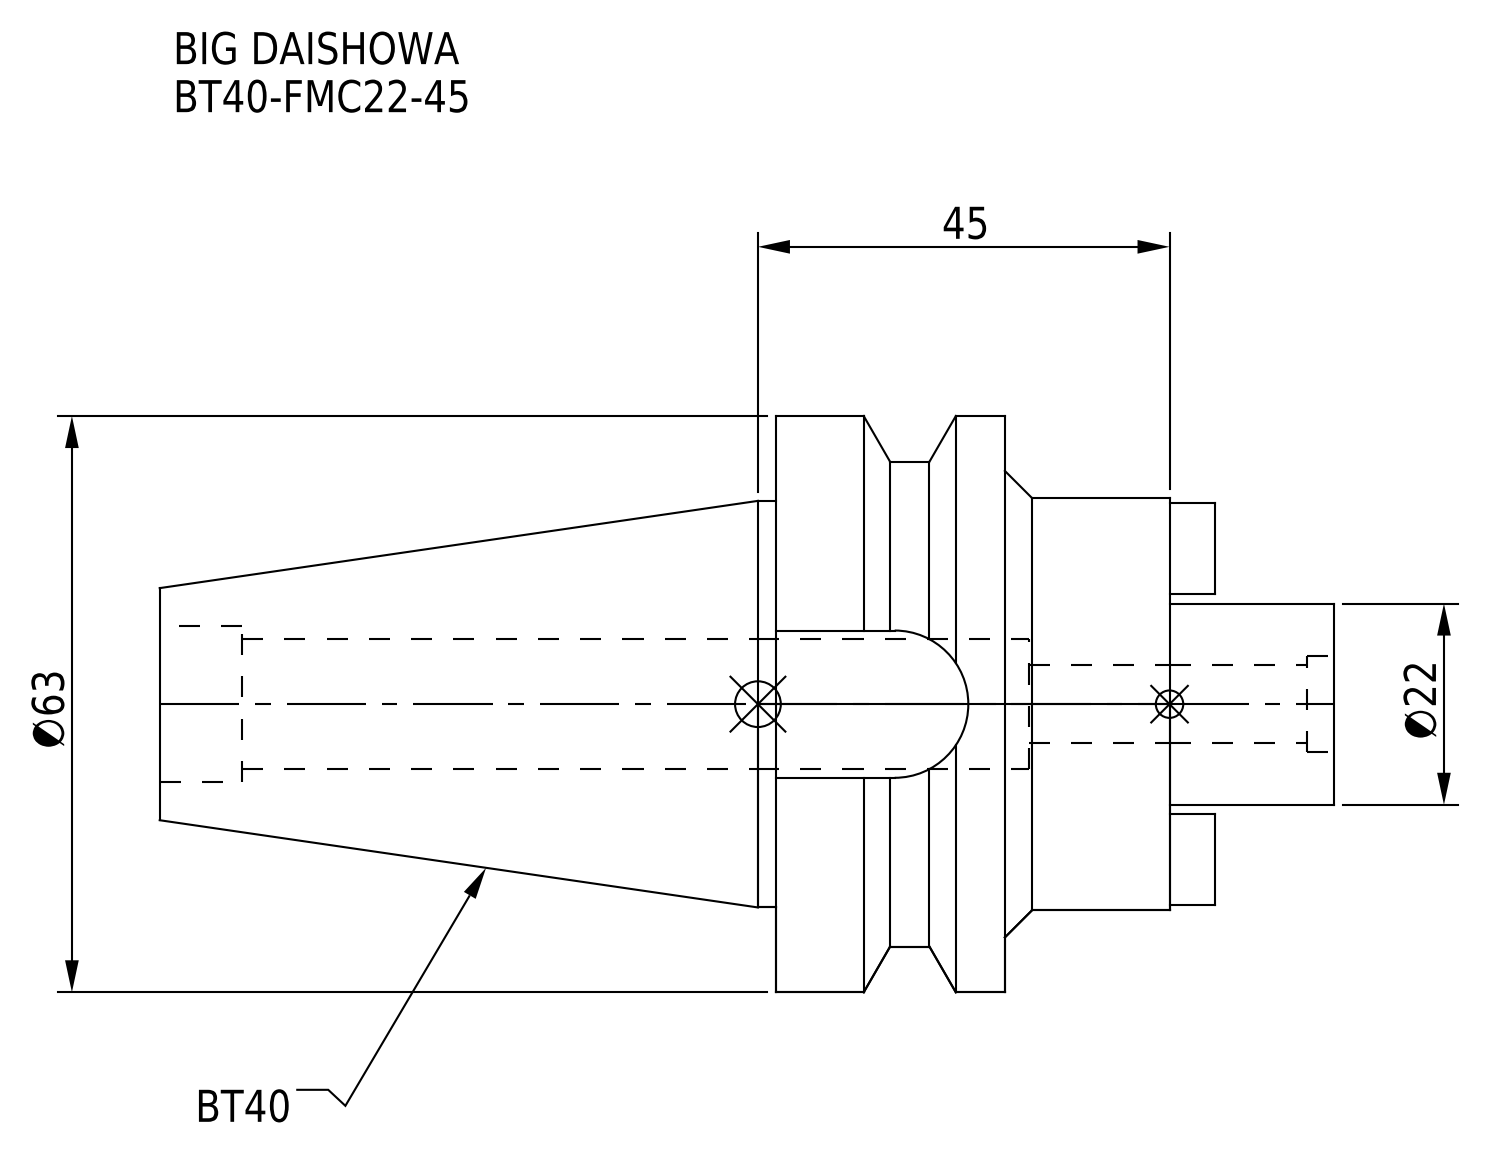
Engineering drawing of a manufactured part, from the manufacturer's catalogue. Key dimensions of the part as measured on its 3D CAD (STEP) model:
Part name (STEP PRODUCT): BT40-FMC22-45
STEP written by: CREO PARAMETRIC BY PTC INC, 2016380 (AUTOMOTIVE_DESIGN)
Units: millimetres
Bodies: 1 solid, 64 faces (30 planar, 26 cylindrical, 8 other)
Overall size (bounding box): 128.4 × 63 × 63
Volume: 153 780 mm³ · Surface area: 27 789 mm²
Round holes (diameter × count): ⌀8.5 ×1, ⌀10.5 ×1, ⌀14.2 ×1, ⌀17 ×1
Round bosses / shafts (diameter × count): ⌀63 ×1, ⌀53 ×1, ⌀45 ×1, ⌀44.45 ×1, ⌀22 ×1
Partial cylindrical surfaces — rounded edges, fillets, slot ends (radius × count): R8.05 ×1
Main face-to-face distances: 18, 25, 43, 45, 36, 61, 128.4, 110.4, 92.4, 67.4
